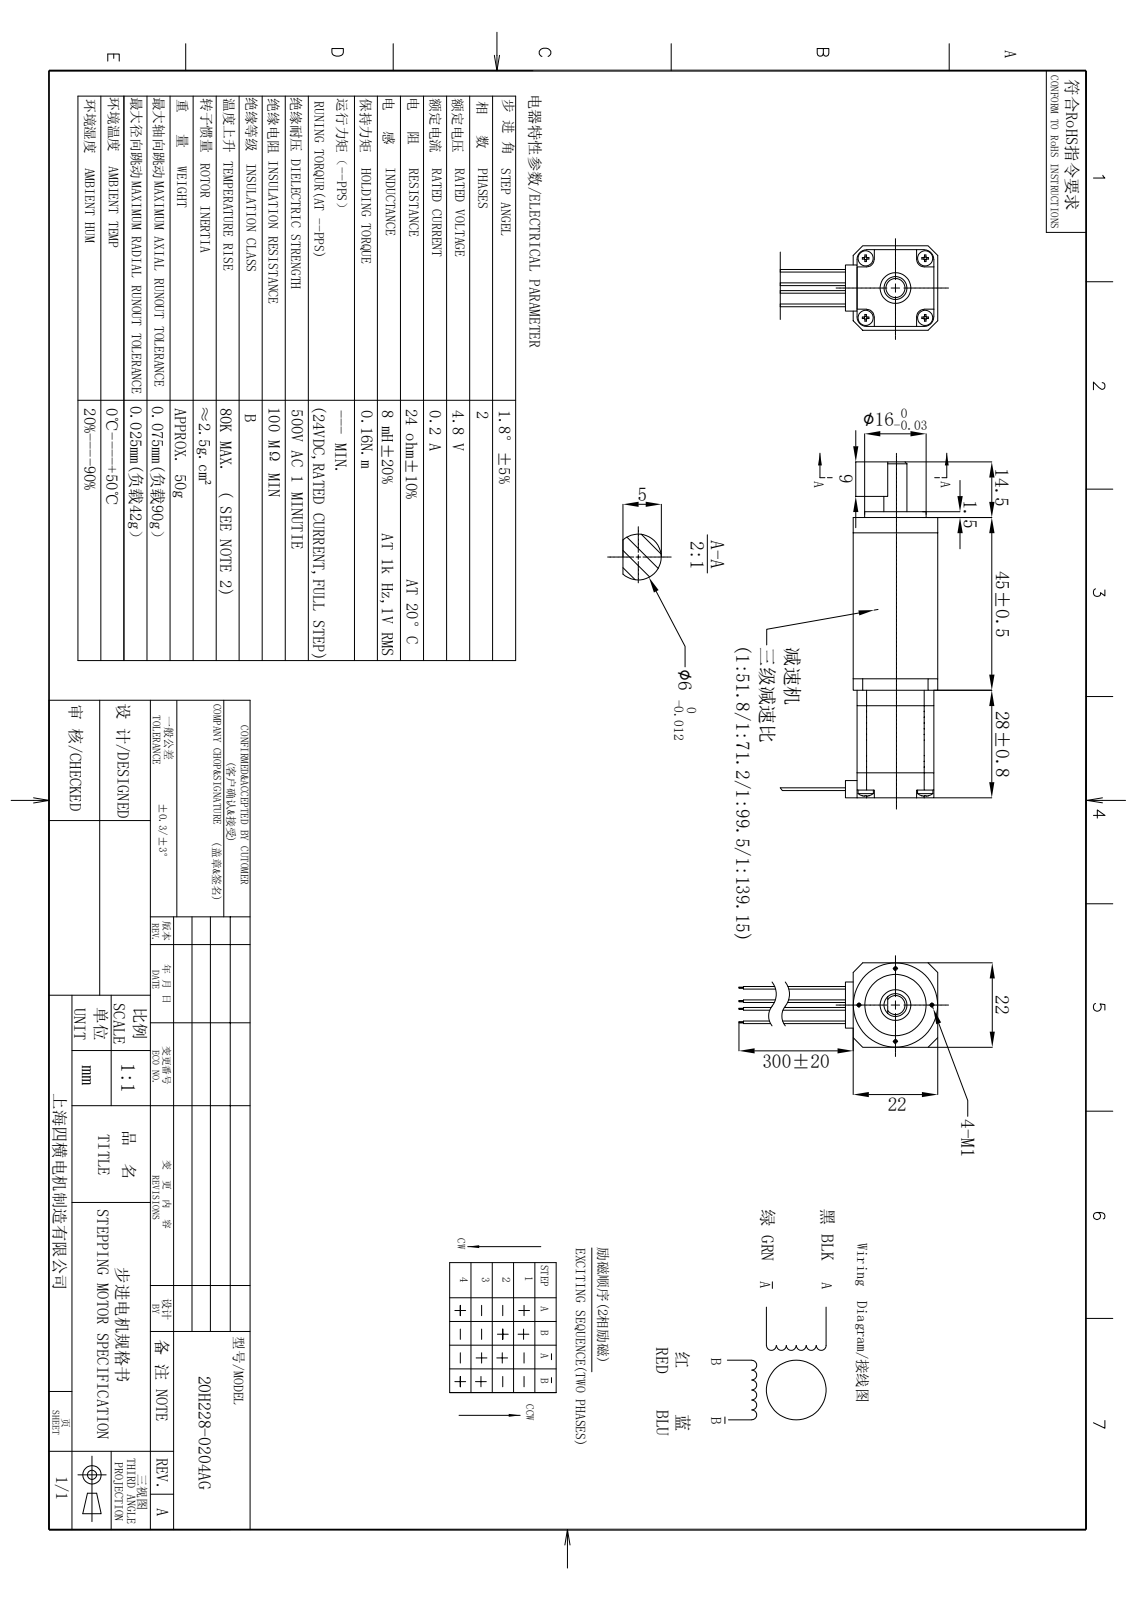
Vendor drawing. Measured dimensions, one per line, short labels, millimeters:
name: 20H228-0204AG51电机; 20H228-0204AG51减速器前端盖; 20H228-0204AG51减速器固定; 20H228-0204AG51 (+8 more)
written by: SolidWorks 2020 (AUTOMOTIVE_DESIGN)
unit: mm
bodies: 20 solids, 752 faces (506 planar, 210 cylindrical, 36 other)
size: 87.5 × 41 × 22
volume: 29 931 mm³; area: 14 329 mm²
holes: 4× ⌀1, 4× ⌀2.5, 1× ⌀8
bosses: 4× ⌀4.5, 4× ⌀4, 4× ⌀2, 4× ⌀0.7, 1× ⌀22, 1× ⌀16, 1× ⌀6
rounds: 16× R0.3, 4× R0.35, 4× R2, 4× R2.45, 4× R2.5
face distances: 4, 45, 3, 20, 41, 38, 7, 62.5, 24.5, 17.5
hole spacings: 7.95, 18.91, 9.5, 10.96, 13.44, 15.5, 19, 21.92
